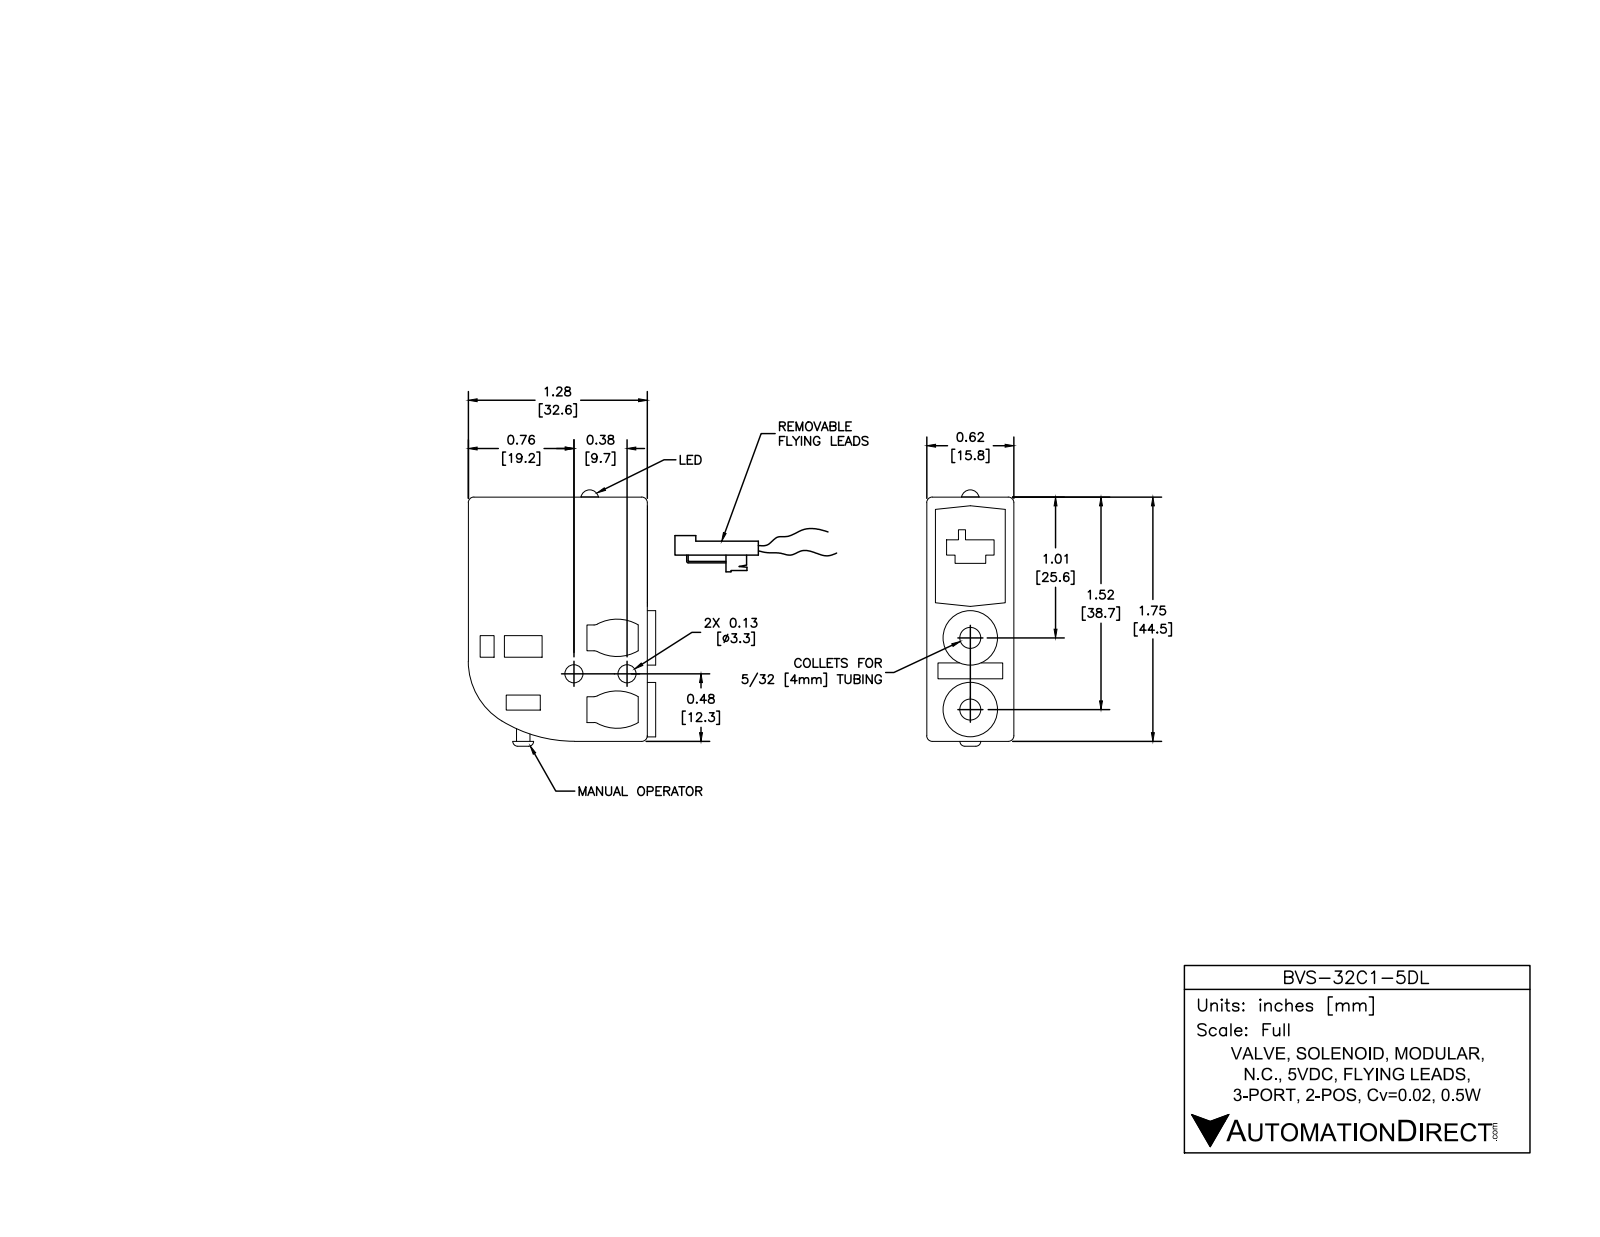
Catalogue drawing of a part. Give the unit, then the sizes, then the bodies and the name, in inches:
Units: inches
Overall size (bounding box): 1.84 × 1.788 × 0.62
Round holes (diameter × count): ⌀0.13 ×2, ⌀0.15 ×2, ⌀0.25 ×2, ⌀0.05 ×1
Round bosses / shafts (diameter × count): ⌀0.06 ×6, ⌀0.39 ×2, ⌀0.1 ×1
Partial cylindrical surfaces — rounded edges, fillets, slot ends (radius × count): R0.05 ×4, R0.3 ×4, R0.04 ×3, R0.5 ×1, R1 ×1
Main face-to-face distances: 0.62, 0.1, 1.29, 0.52, 1.291, 1.75, 1, 0.15, 0.06, 1.35
Hole centre spacings: 0.06, 0.38, 0.45, 0.51
Volume: 1.259 in³ · Surface area: 10.37 in²
Bodies: 1 solid, 149 faces (83 planar, 54 cylindrical, 12 other)
Part name (STEP PRODUCT): BVS-32C1-5DL
STEP written by: SolidWorks 2016 (AUTOMOTIVE_DESIGN)
